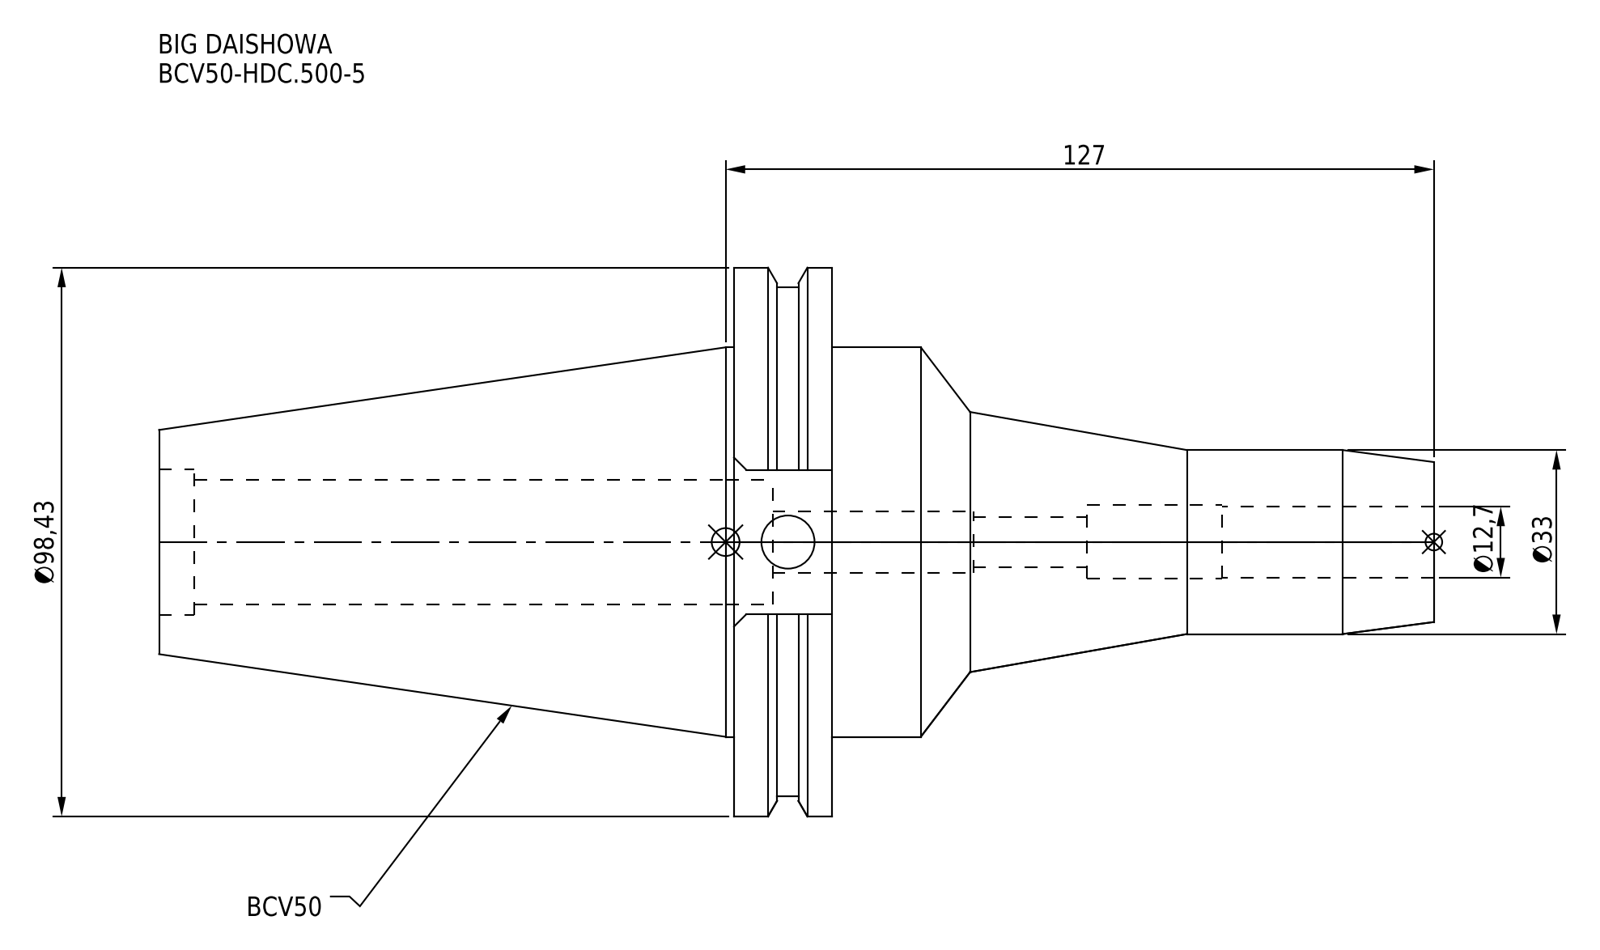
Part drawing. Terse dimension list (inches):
name: BCV50-HDC_500-5
written by: CREO PARAMETRIC BY PTC INC, 2016380 (AUTOMOTIVE_DESIGN)
unit: in
bodies: 1 solid, 64 faces (24 planar, 28 cylindrical, 12 other)
size: 9 × 3.875 × 3.738
volume: 29.56 in³; area: 94.6 in²
holes: 1× ⌀0.354, 1× ⌀0.375, 1× ⌀0.433, 1× ⌀0.5, 1× ⌀0.52, 1× ⌀0.878, 1× ⌀1.033
bosses: 1× ⌀3.875, 1× ⌀3.594, 1× ⌀2.75, 1× ⌀1.299
face distances: 0.691, 4.75, 4.059, 4.25, 4.941, 9, 2.872, 1.02, 4.669, 0.419
